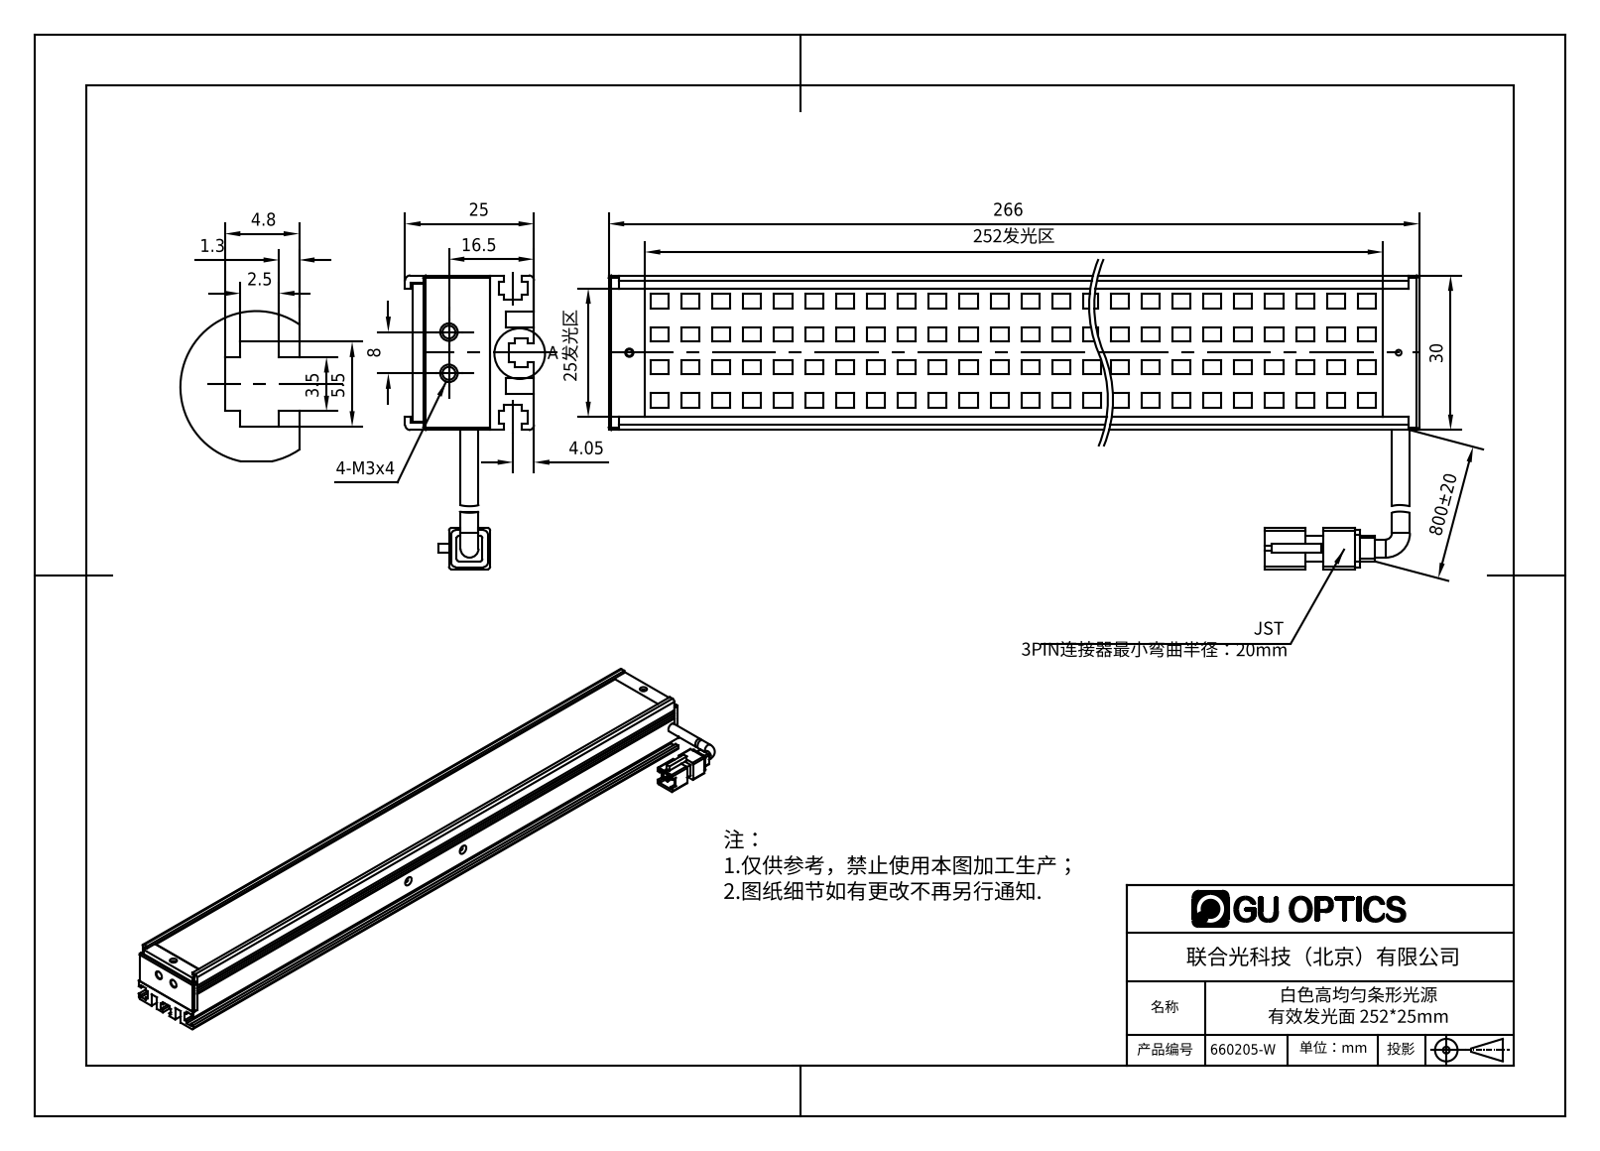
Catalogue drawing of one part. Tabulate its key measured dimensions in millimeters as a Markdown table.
| quantity | value |
| --- | --- |
| part name | 660205-W |
| STEP written by | SolidWorks 2016 (AUTOMOTIVE_DESIGN) |
| units | millimeters |
| bodies | 6 solids, 1284 faces (1098 planar, 83 cylindrical, 103 other) |
| overall size | 266 × 57 × 25 |
| volume | 90 767 mm³ |
| surface area | 92 489 mm² |
| round holes (diameter × count) | 1.6 × 5, 1.5 × 2, 1.7 × 2, 2.5 × 2, 2.8 × 2, 3 × 2, 1.1 × 1, 1.25 × 1, 2 × 1 |
| round bosses / shafts (diameter × count) | 3.5 × 2 |
| partial cylindrical surfaces (radius × count) | 1 × 12, 0.5 × 8, 1.65 × 1 |
| main face-to-face distances | 1, 13, 2, 2.5, 3, 27.5, 9.5, 4.5, 12, 15.1 |
| hole center spacings | 258, 7, 114, 114.19, 144, 144.15, 258.09, 8 |
